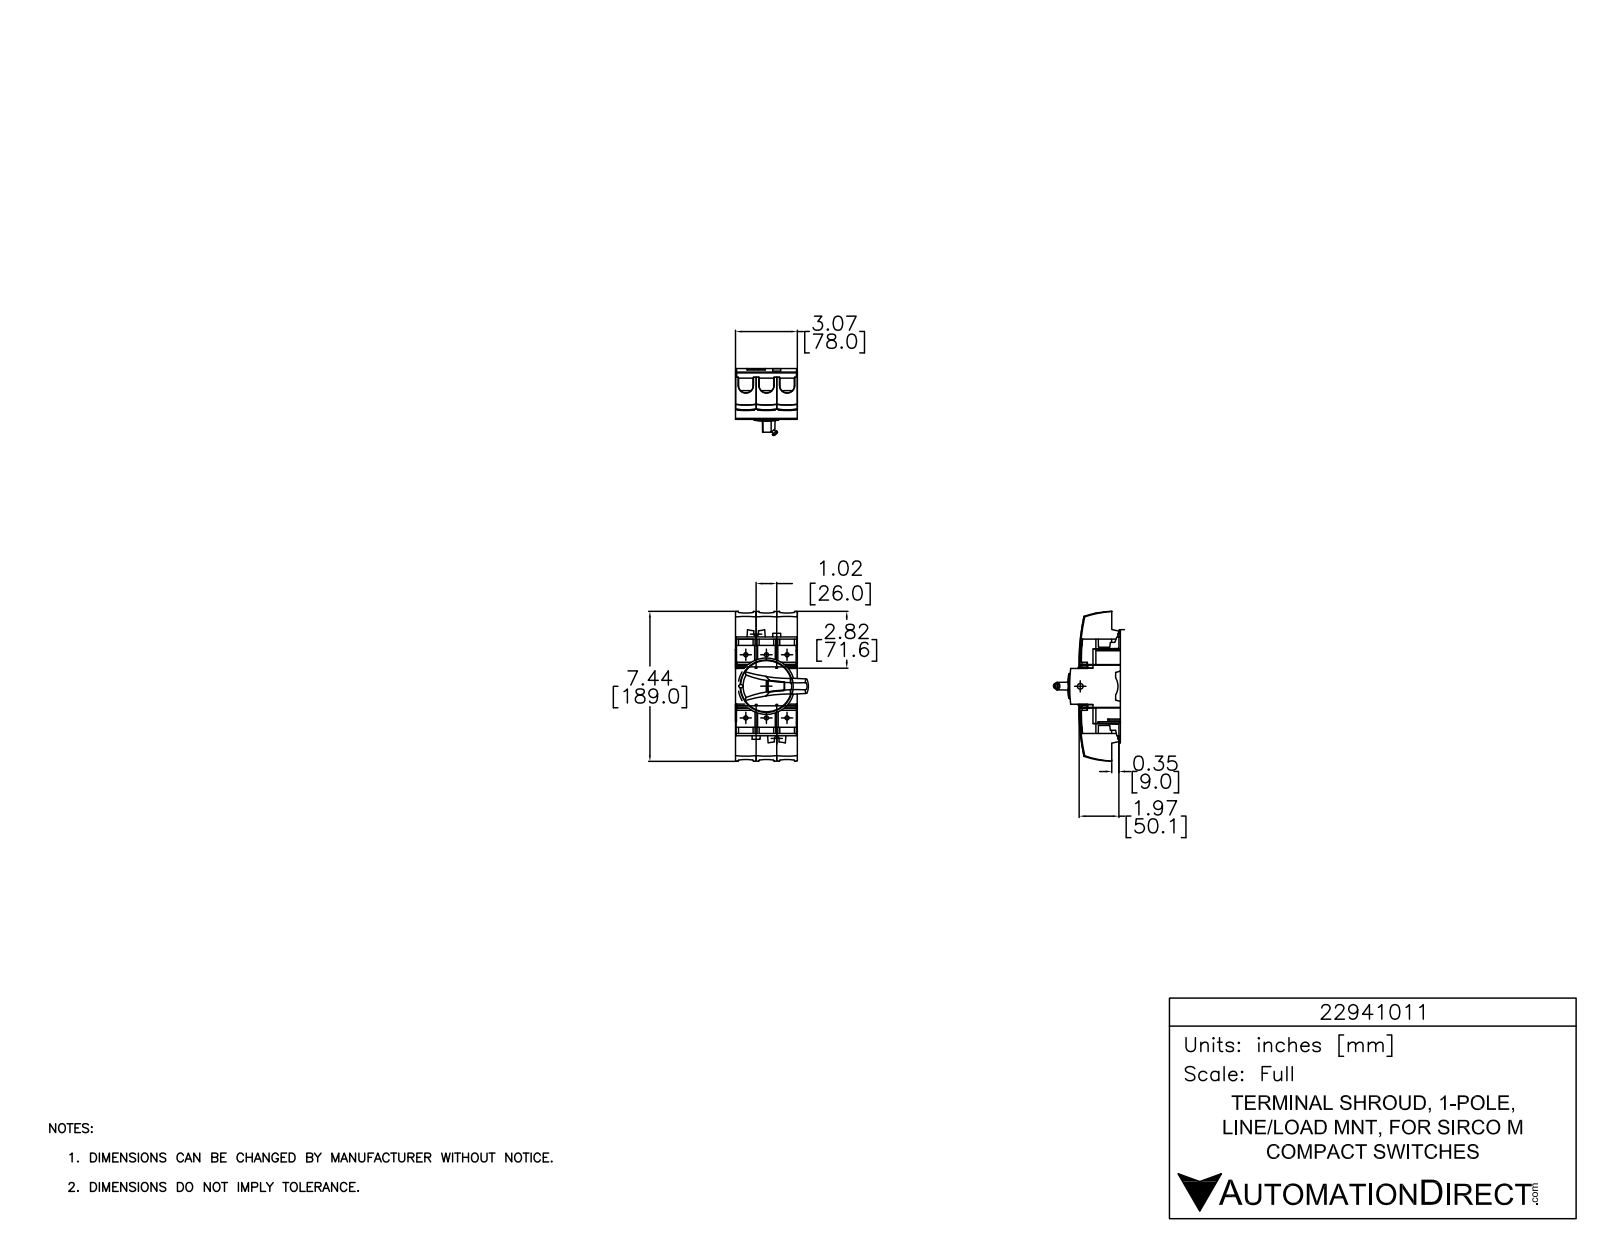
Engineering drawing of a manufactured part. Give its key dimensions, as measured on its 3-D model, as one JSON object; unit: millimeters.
{"part_name": "22941011", "step_written_by": "SolidWorks 2015 (AUTOMOTIVE_DESIGN)", "units": "millimeters", "bodies": {"solids": 1, "faces": 45, "planar": 33, "cylindrical": 2, "other": 10}, "overall_size": [40, 32.1, 15], "volume_mm3": 2880, "surface_area_mm2": 5011, "partial_cylinders_radius": [[4.8, 1], [5.8, 1]], "face_to_face_distances": [1.2, 13.8, 15, 12.6, 2.7, 12.3, 1.5, 11.1, 9.6, 4]}
